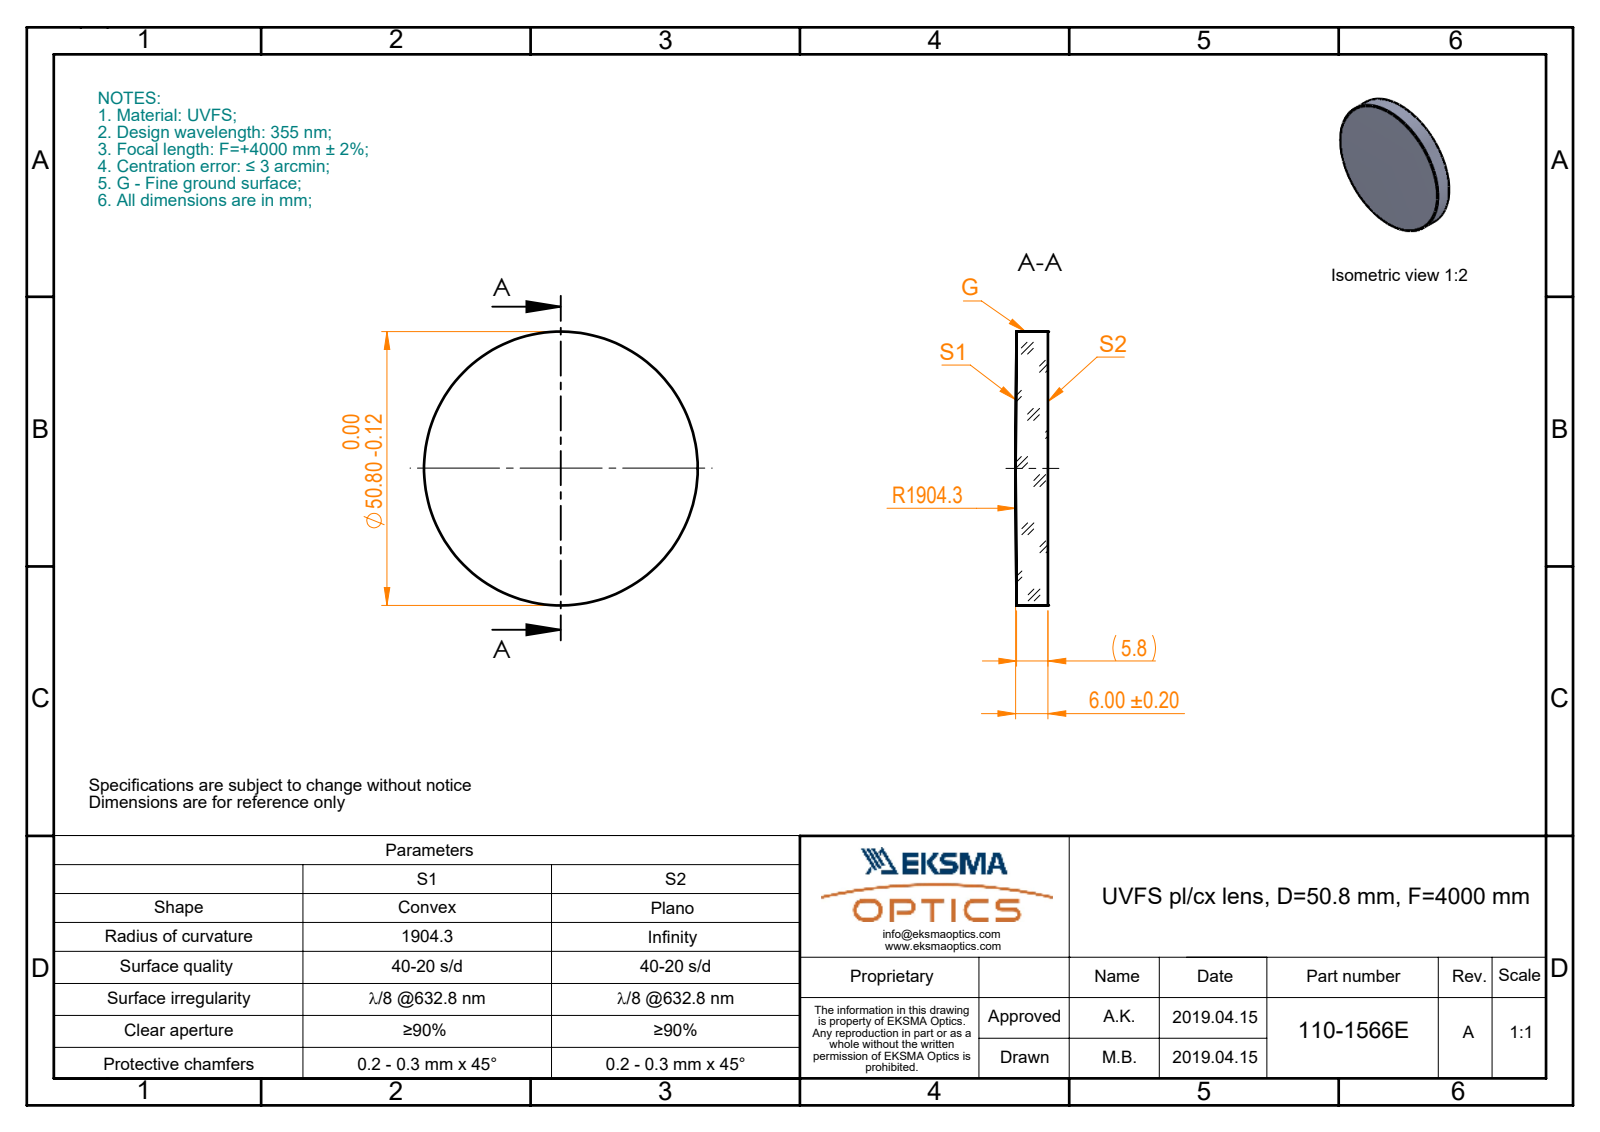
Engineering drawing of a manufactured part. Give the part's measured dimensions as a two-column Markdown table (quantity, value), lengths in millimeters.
| quantity | value |
| --- | --- |
| part name | 110-1566E UVFS pl-cx 50.8 F4000 |
| STEP written by | SolidWorks 2017 (CONFIG_CONTROL_DESIGN) |
| units | millimeters |
| bodies | 1 solid, 5 faces (1 planar, 2 cylindrical, 2 other) |
| overall size | 50.8 × 50.8 × 6 |
| volume | 11 989 mm³ |
| surface area | 4 984 mm² |
| round bosses / shafts (diameter × count) | 50.8 × 1 |
